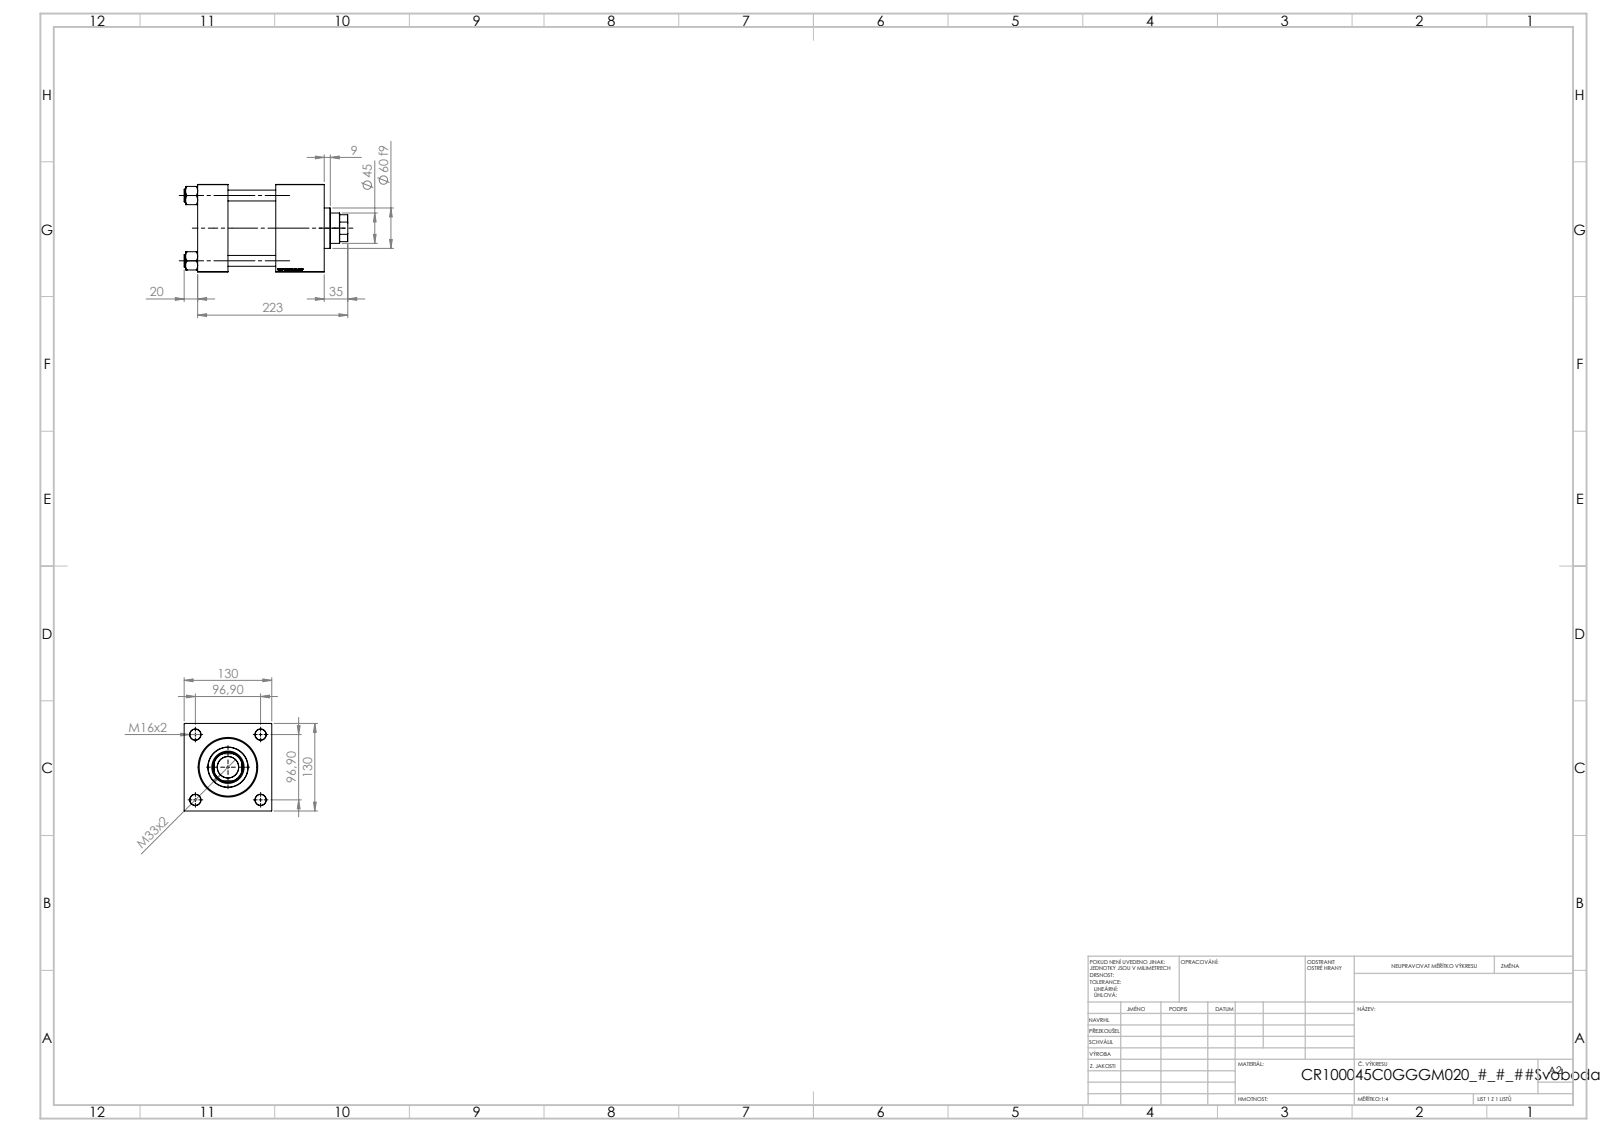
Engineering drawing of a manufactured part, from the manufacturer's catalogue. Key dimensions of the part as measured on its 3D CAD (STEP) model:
Part name (STEP PRODUCT): NUT_M5_C; V215CR_C_TYCINKA; V215CR_C_Body; V215_VC_A (+1 more)
STEP written by: SolidWorks 2019 (CONFIG_CONTROL_DESIGN)
Units: millimetres
Bodies: 11 solids, 1197 faces (574 planar, 87 cylindrical, 536 other)
Overall size (bounding box): 243 × 130 × 130
Volume: 2 425 000 mm³ · Surface area: 326 396 mm²
Round holes (diameter × count): ⌀16 ×4, ⌀7 ×2, ⌀26.44 ×2, ⌀35 ×2, ⌀31.5 ×1, ⌀45 ×1, ⌀48 ×1, ⌀76 ×1, ⌀85.5 ×1, ⌀100 ×1
Round bosses / shafts (diameter × count): ⌀19 ×4, ⌀106 ×1, ⌀60 ×1
Partial cylindrical surfaces — rounded edges, fillets, slot ends (radius × count): R22 ×1
Main face-to-face distances: 130, 45, 188, 143, 116, 71, 72, 20, 96, 51
Hole centre spacings: 68.52, 96.9, 137.04, 118.5
